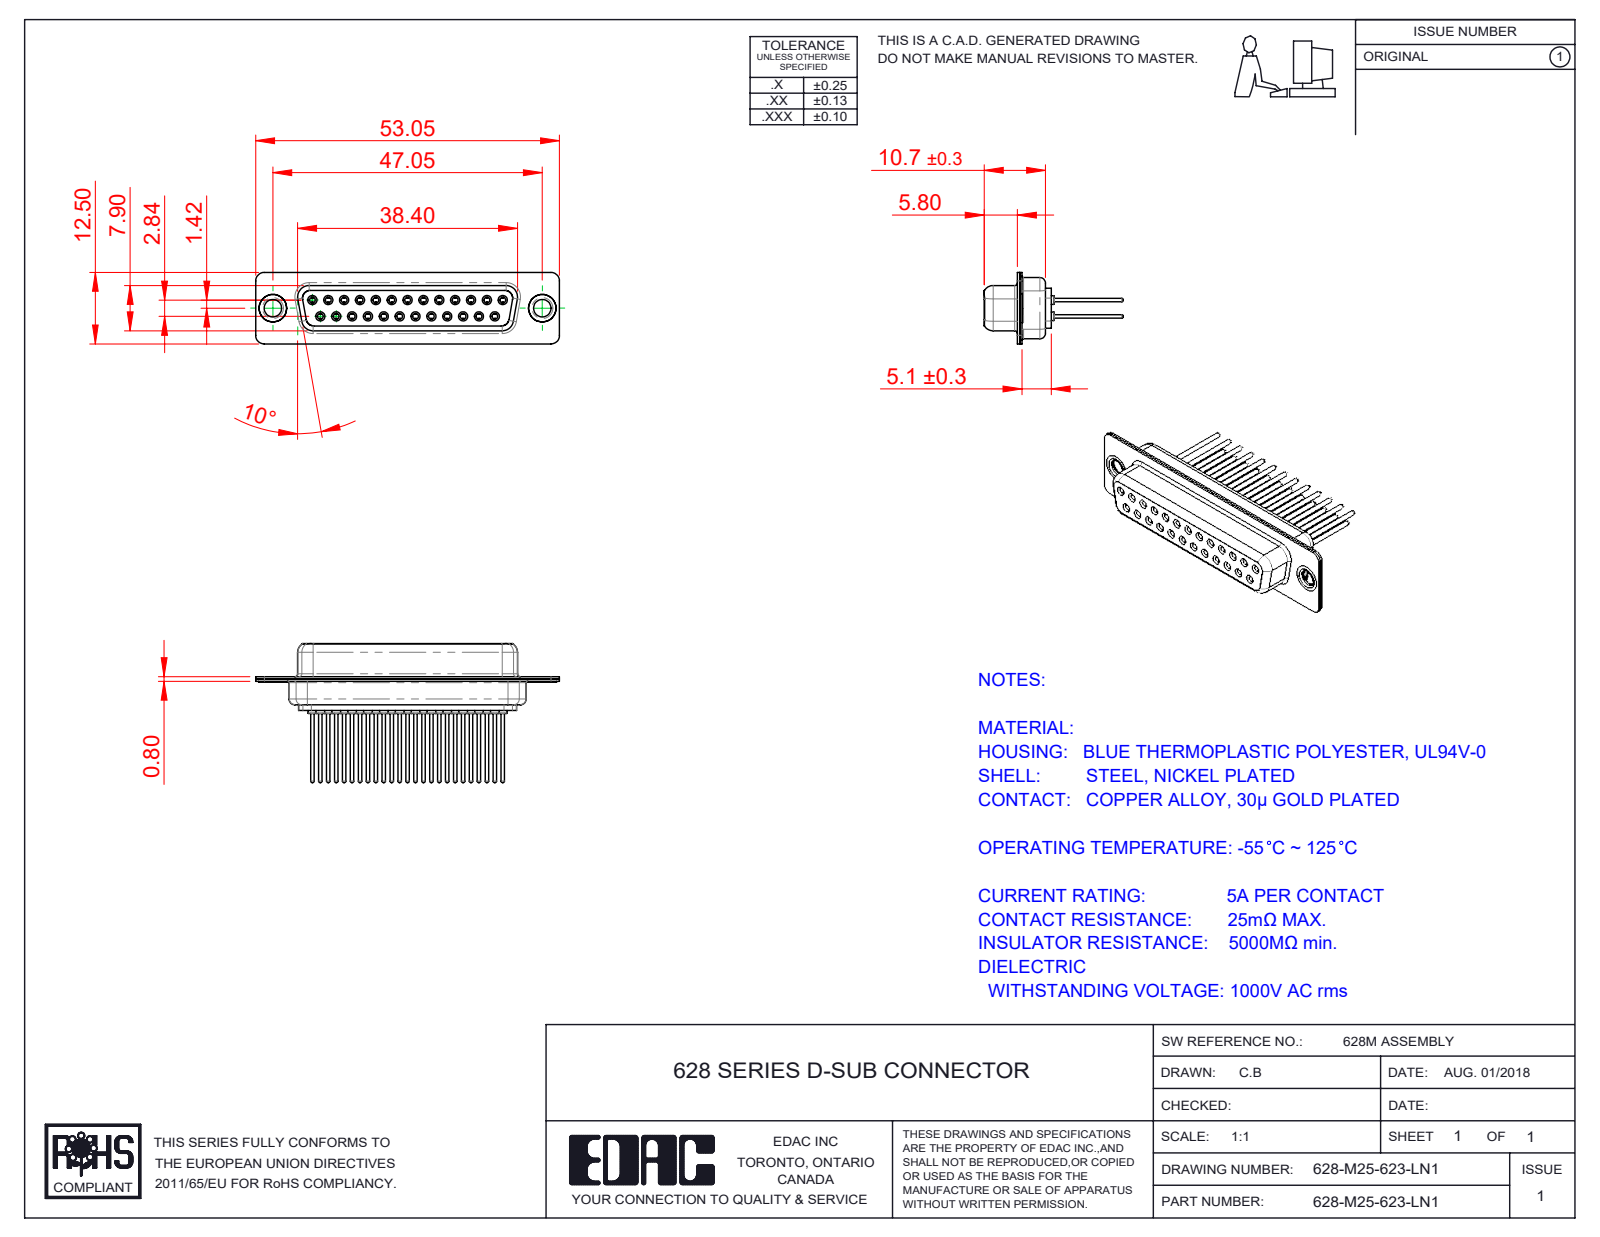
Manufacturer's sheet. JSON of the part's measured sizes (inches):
{"part_name": "628M Housing_25 Contacts; 628M Contact Row 1_23; 628M Contact Row 2_23; 628-M25-623-LN1 (+3 more)", "step_written_by": "SolidWorks 2020 (CONFIG_CONTROL_DESIGN)", "units": "inches", "bodies": {"solids": 30, "faces": 1628, "planar": 442, "cylindrical": 596, "other": 590}, "overall_size": [2.089, 0.956, 0.492], "volume_in3": 0.226, "surface_area_in2": 14.44, "round_holes": [[0.039, 25], [0.043, 25], [0.067, 25], [0.071, 25], [0.079, 25], [0.12, 2], [0.157, 2], [0.189, 2]], "round_bosses_or_shafts": [[0.087, 25], [0.063, 25], [0.059, 25], [0.024, 25], [0.197, 2], [0.193, 2], [0.14, 2]], "partial_cylinders_radius": [[0.059, 16], [0.079, 12], [0.053, 8], [0.063, 8], [0.01, 4], [0.02, 4], [0.024, 4], [0.026, 4]], "face_to_face_distances": [0.016, 0.055, 0.018, 0.333, 0.35, 0.244, 0.071, 0.278, 0.039, 0.073], "hole_center_spacings": [0.124, 0.109, 0.218, 0.327, 0.436, 0.545, 0.198, 0.295]}
